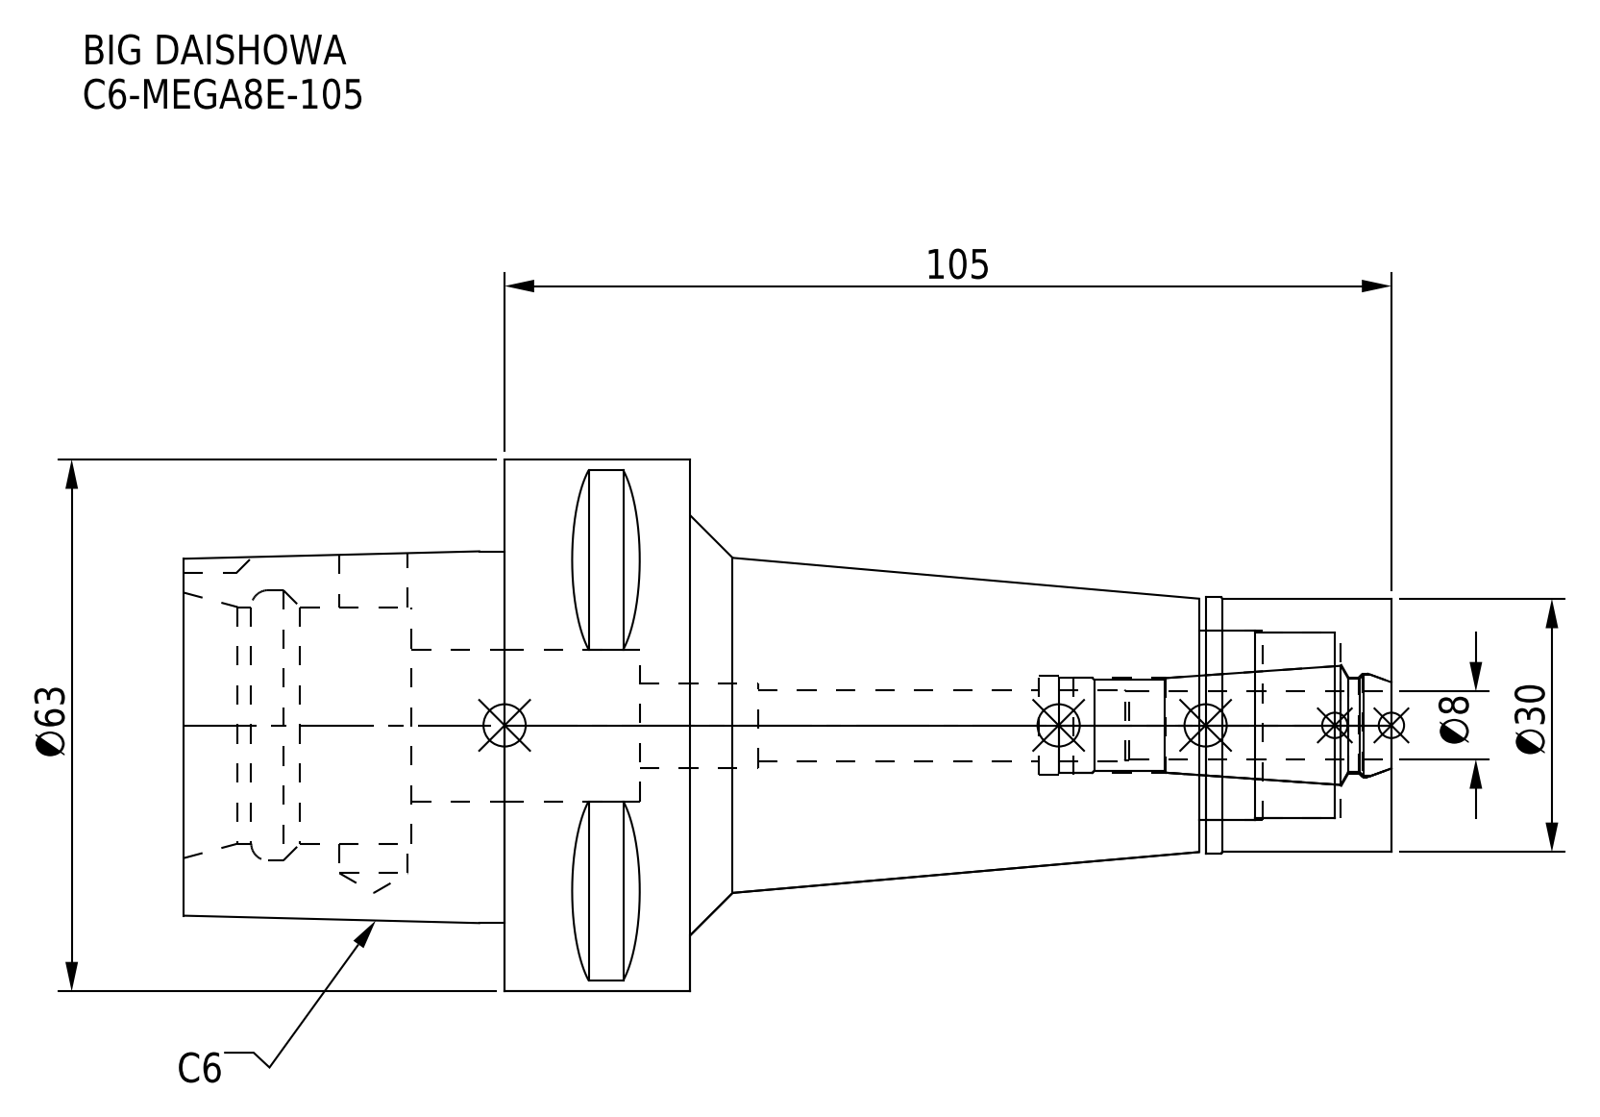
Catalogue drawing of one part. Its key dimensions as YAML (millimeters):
part_name: "C6-MEGA8E-105_1.stp; DXF_TEMP_ASSY_ASM_4_ASM.stp; C6-MEGA8E-105-080_ASM.stp; MEN8_1.stp (+3 more)"
step_written_by: "SolidWorks 2019 (CONFIG_CONTROL_DESIGN)"
units: millimeters
bodies: {solids: 2, faces: 100, planar: 37, cylindrical: 39, other: 24}
overall_size: [143, 63, 63]
volume: 165376
surface_area: 34241
round_holes:
  - {diameter: 8.1, count: 1}
  - {diameter: 8.4, count: 1}
  - {diameter: 10, count: 1}
  - {diameter: 11.2, count: 1}
  - {diameter: 11.4, count: 1}
  - {diameter: 11.8, count: 1}
  - {diameter: 12.3, count: 1}
  - {diameter: 18, count: 1}
  - {diameter: 22, count: 1}
  - {diameter: 22.5, count: 1}
  - {diameter: 28, count: 1}
  - {diameter: 32, count: 1}
round_bosses_or_shafts:
  - {diameter: 63, count: 1}
  - {diameter: 30.3, count: 1}
  - {diameter: 30, count: 1}
partial_cylinders:
  - {radius: 5, count: 1}
face_to_face_distances: [22, 83, 105, 27, 143, 60, 38, 6, 16, 116]
